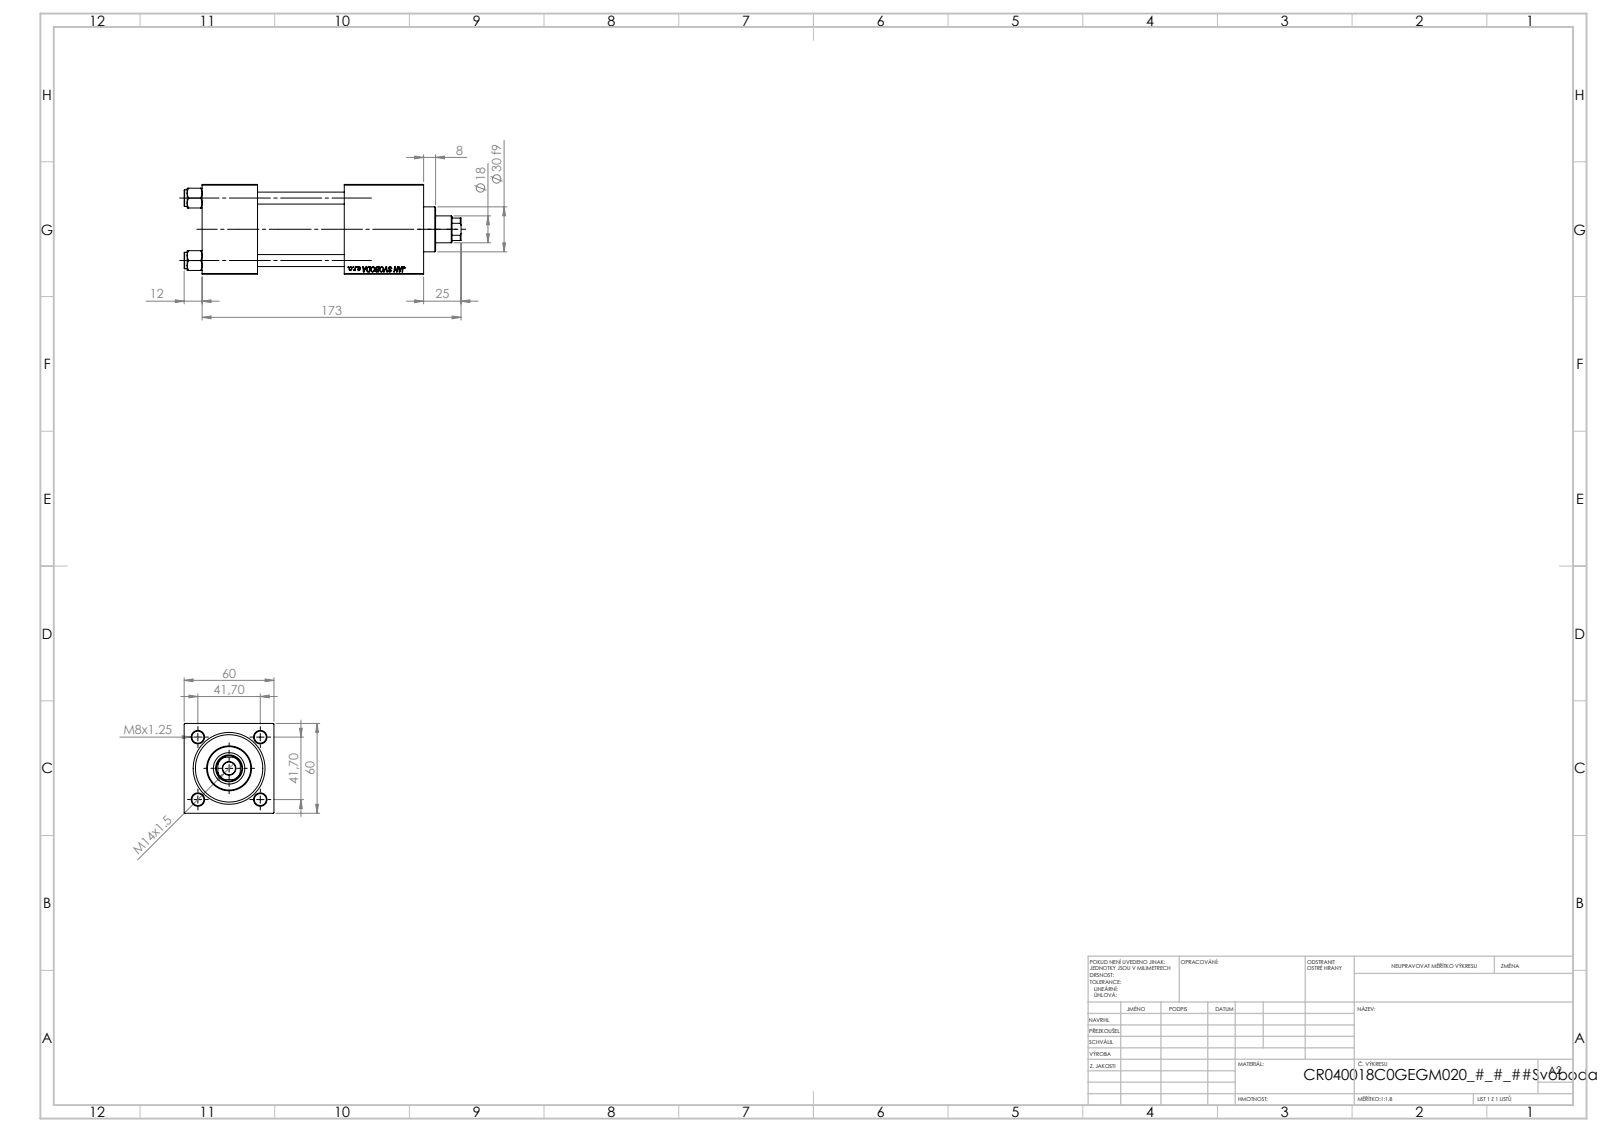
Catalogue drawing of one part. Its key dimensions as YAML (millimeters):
part_name: "V215CR_C_TYCINKA; NUT_M5_C; V215_VC_A; V215CR_VCP_C (+1 more)"
step_written_by: "SolidWorks 2019 (CONFIG_CONTROL_DESIGN)"
units: millimeters
bodies: {solids: 11, faces: 1149, planar: 526, cylindrical: 87, other: 536}
overall_size: [185, 60, 60]
volume: 402490
surface_area: 105329
round_holes:
  - {diameter: 8, count: 4}
  - {diameter: 7, count: 2}
  - {diameter: 16.66, count: 2}
  - {diameter: 24, count: 2}
  - {diameter: 8.5, count: 1}
  - {diameter: 18, count: 1}
  - {diameter: 21, count: 1}
  - {diameter: 31, count: 1}
  - {diameter: 40, count: 1}
  - {diameter: 45, count: 1}
round_bosses_or_shafts:
  - {diameter: 11, count: 4}
  - {diameter: 46, count: 1}
  - {diameter: 30, count: 1}
partial_cylinders:
  - {radius: 8.5, count: 1}
face_to_face_distances: [60, 37, 53, 148, 111, 58, 95, 119.3, 82.3, 24.3]
hole_center_spacings: [29.49, 41.7, 58.97, 92.5]
